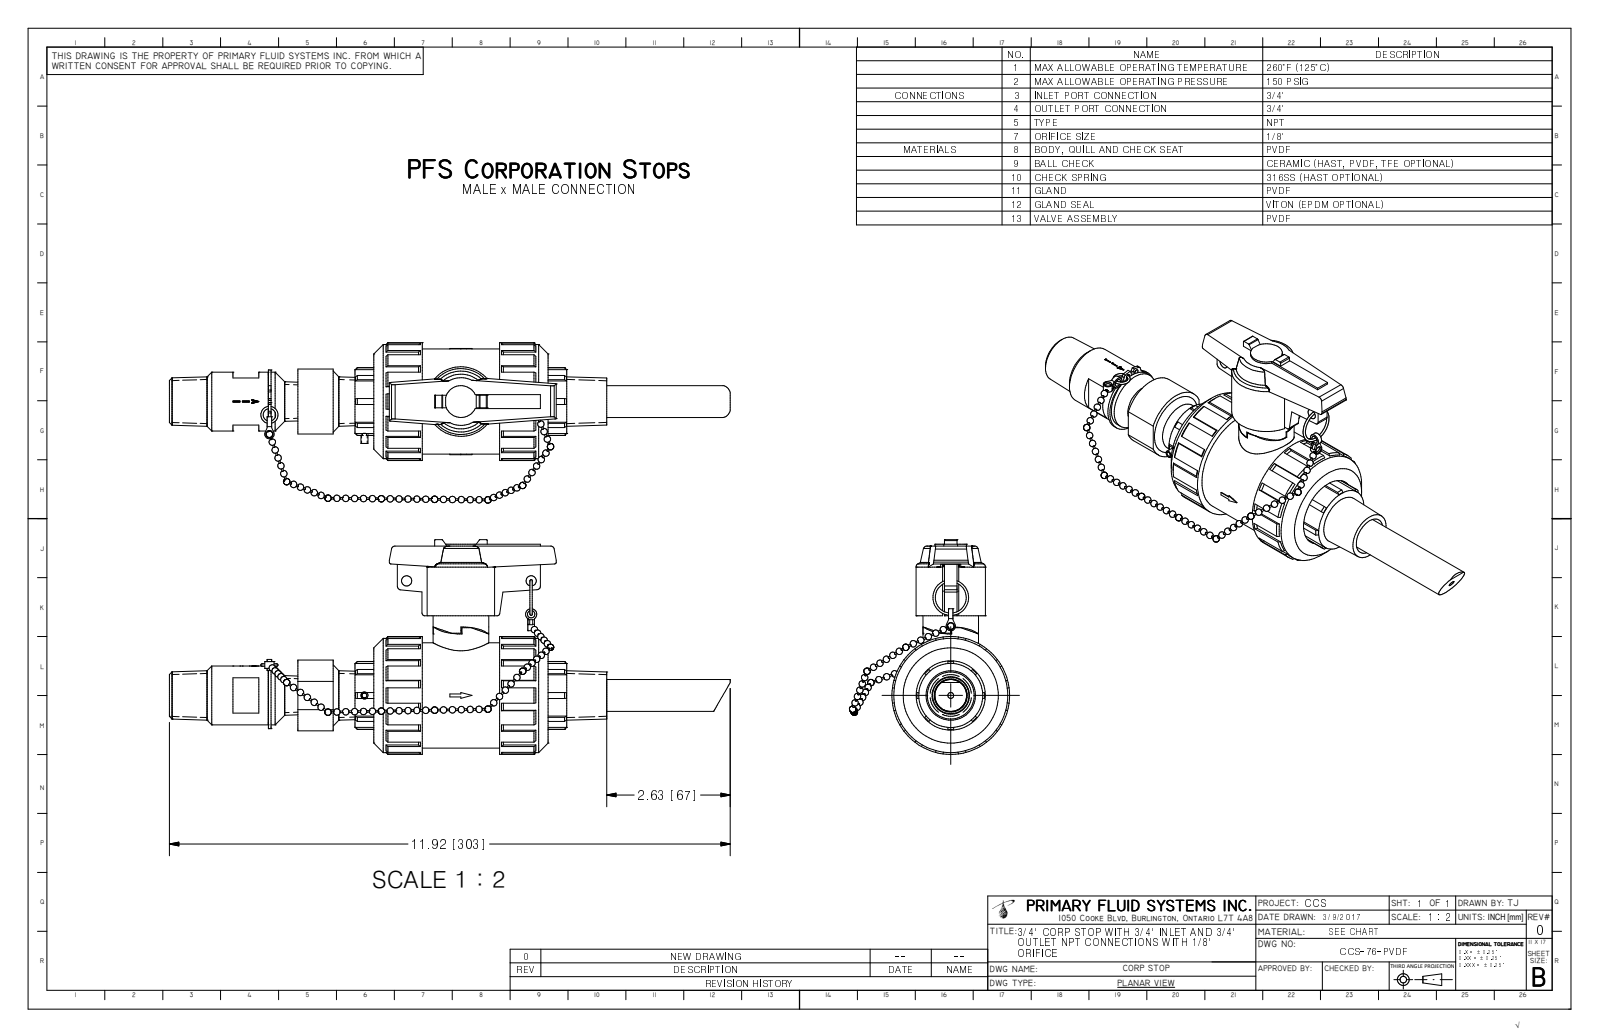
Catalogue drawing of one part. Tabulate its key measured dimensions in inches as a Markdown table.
| quantity | value |
| --- | --- |
| part name | CCS-76-PVDF_R0 |
| STEP written by | Autodesk Inventor 2009 (AUTOMOTIVE_DESIGN) |
| units | inches |
| bodies | 1 solid, 601 faces (293 planar, 78 cylindrical, 230 other) |
| overall size | 11.922 × 4.554 × 3.404 |
| volume | 26.14 in³ |
| surface area | 119.5 in² |
| round holes (diameter × count) | 0.098 × 1, 0.125 × 1, 0.217 × 1, 0.25 × 1, 0.469 × 1, 0.56 × 1, 1.47 × 1, 2.16 × 1 |
| round bosses / shafts (diameter × count) | 2.5 × 1, 2.422 × 1, 2.232 × 1, 1.801 × 1, 1.476 × 1, 1.36 × 1, 1.343 × 1, 1.25 × 1 |
| partial cylindrical surfaces (radius × count) | 0.02 × 4, 0.079 × 4, 0.039 × 2, 0.054 × 2, 0.059 × 2, 0.197 × 2, 0.337 × 1, 0.624 × 1 |
| main face-to-face distances | 0.039, 0.266, 0.306, 0.472, 3.233, 0.23, 3.475, 0.242, 3.003, 1.03 |
| hole center spacings | 0.657 |
